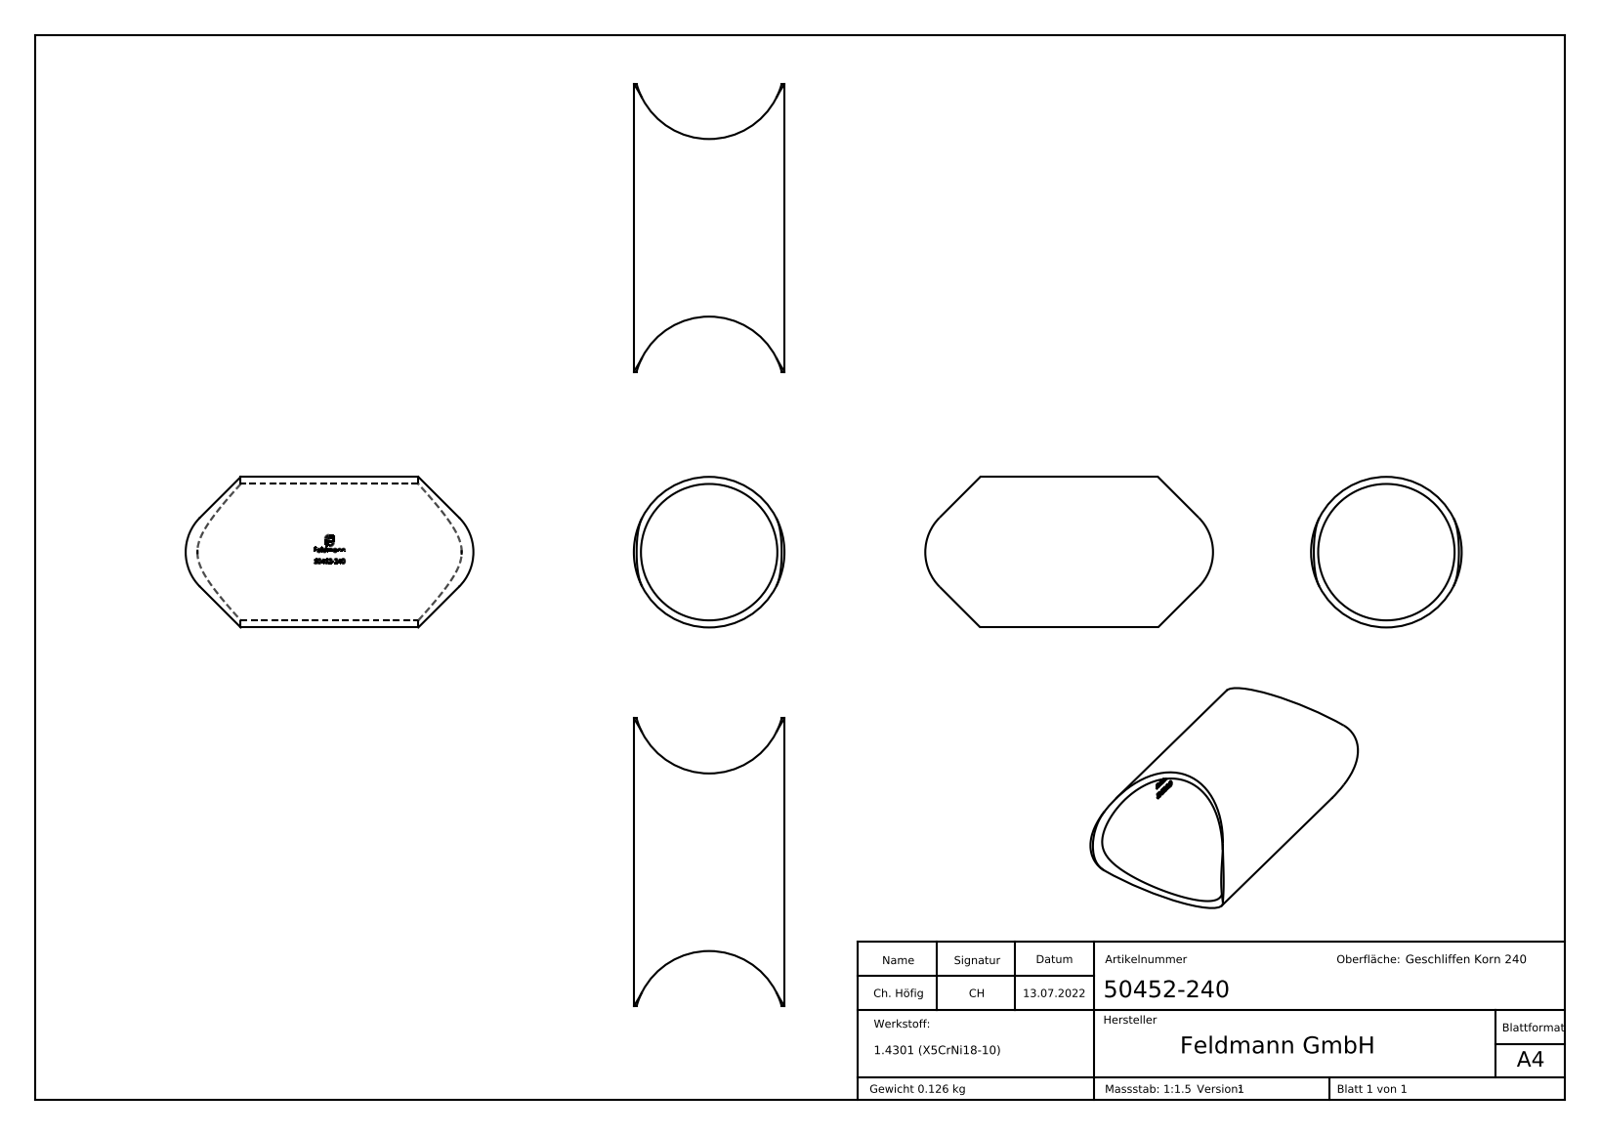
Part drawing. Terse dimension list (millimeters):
name: 50452-240
written by: SolidWorks 2018 (CONFIG_CONTROL_DESIGN)
unit: mm
bodies: 1 solid, 277 faces (130 planar, 33 cylindrical, 114 other)
size: 81 × 42.4 × 42.4
volume: 15 927 mm³; area: 16 683 mm²
holes: 1× ⌀38.4
bosses: 1× ⌀42.4
rounds: 2× R13.76, 2× R21.2, 1× R19.3
face distances: 4.39, 1.82, 2.9, 0.88, 3.27, 0.92, 0.34, 2.74, 3.21, 7.75
